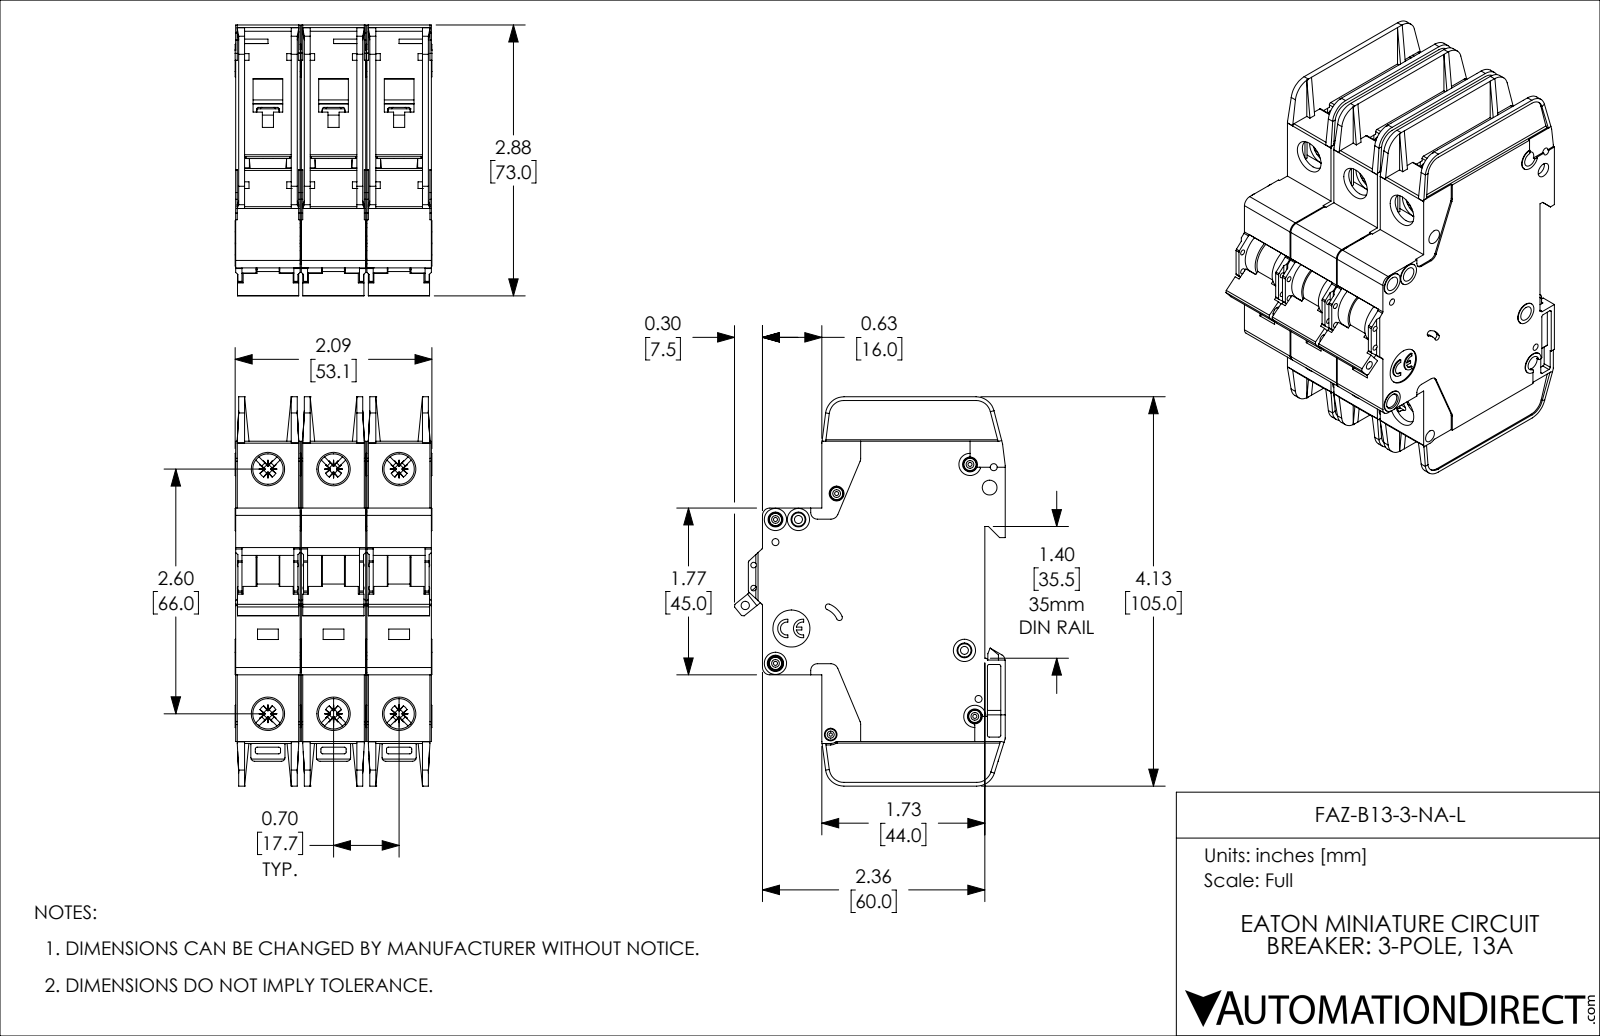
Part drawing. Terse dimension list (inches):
name: FAZ-B13-3-NA-L
written by: SolidWorks 2019 (AUTOMOTIVE_DESIGN)
unit: in
bodies: 3 solids, 3381 faces (2013 planar, 1071 cylindrical, 297 other)
size: 4.134 × 2.876 × 2.091
volume: 14.05 in³; area: 123 in²
holes: 8× ⌀0.157, 6× ⌀0.323, 5× ⌀0.043, 4× ⌀0.075, 2× ⌀0.059, 2× ⌀0.085, 1× ⌀0.035, 1× ⌀0.089, 1× ⌀0.098, 1× ⌀0.134, 1× ⌀0.394
bosses: 5× ⌀0.13, 4× ⌀0.236, 4× ⌀0.118, 3× ⌀0.098
rounds: 72× R0.02, 30× R0.016, 18× R0.039, 12× R0.043, 12× R0.079, 6× R0.008, 6× R0.01, 6× R0.028
face distances: 0.697, 0.047, 1.394, 0.685, 0.591, 1.382, 0.744, 0.65, 0.106, 0.094
hole spacings: 0.697, 2.69, 2.598, 0.244, 0.537, 0.87, 1.394, 2.948
